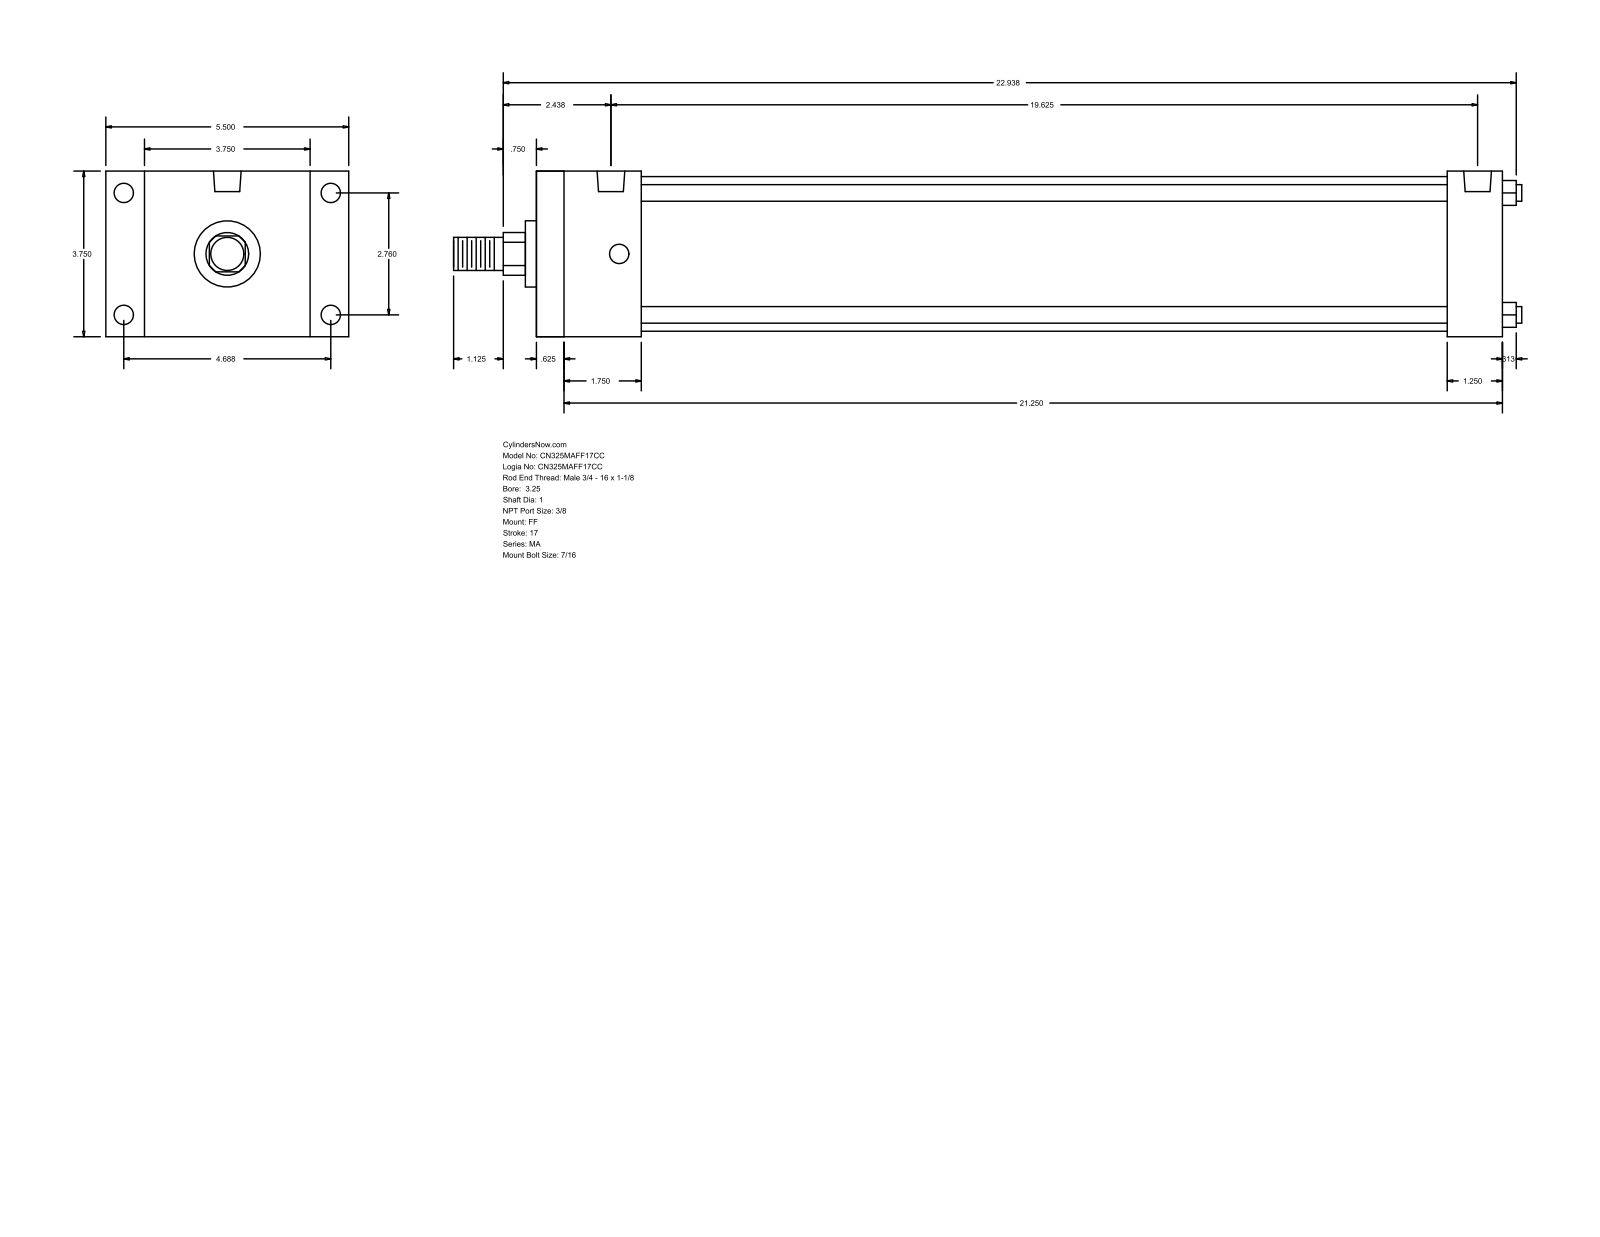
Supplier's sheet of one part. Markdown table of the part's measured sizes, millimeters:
| quantity | value |
| --- | --- |
| part name | MA_FF__0325_1 |
| STEP written by | GSSL Pune (CONFIG_CONTROL_DESIGN) |
| units | millimeters |
| bodies | 0 solids, 92 faces (64 planar, 28 cylindrical, 0 other) |
| overall size | 614.36 × 139.7 × 95.25 |
| round holes (diameter × count) | 11.11 × 8, 15.93 × 2 |
| round bosses / shafts (diameter × count) | 9.53 × 4, 88.9 × 1, 38.1 × 1, 25.4 × 1, 19.05 × 1 |
| partial cylindrical surfaces (radius × count) | 12.29 × 1 |
| main face-to-face distances | 95.24, 555.62, 15.87, 539.75, 22.23, 117.47, 60.33, 523.87, 44.46, 508 |
| hole center spacings | 70.1, 119.06, 138.16, 488.95, 4.76, 4.77, 493.71, 493.72 |
